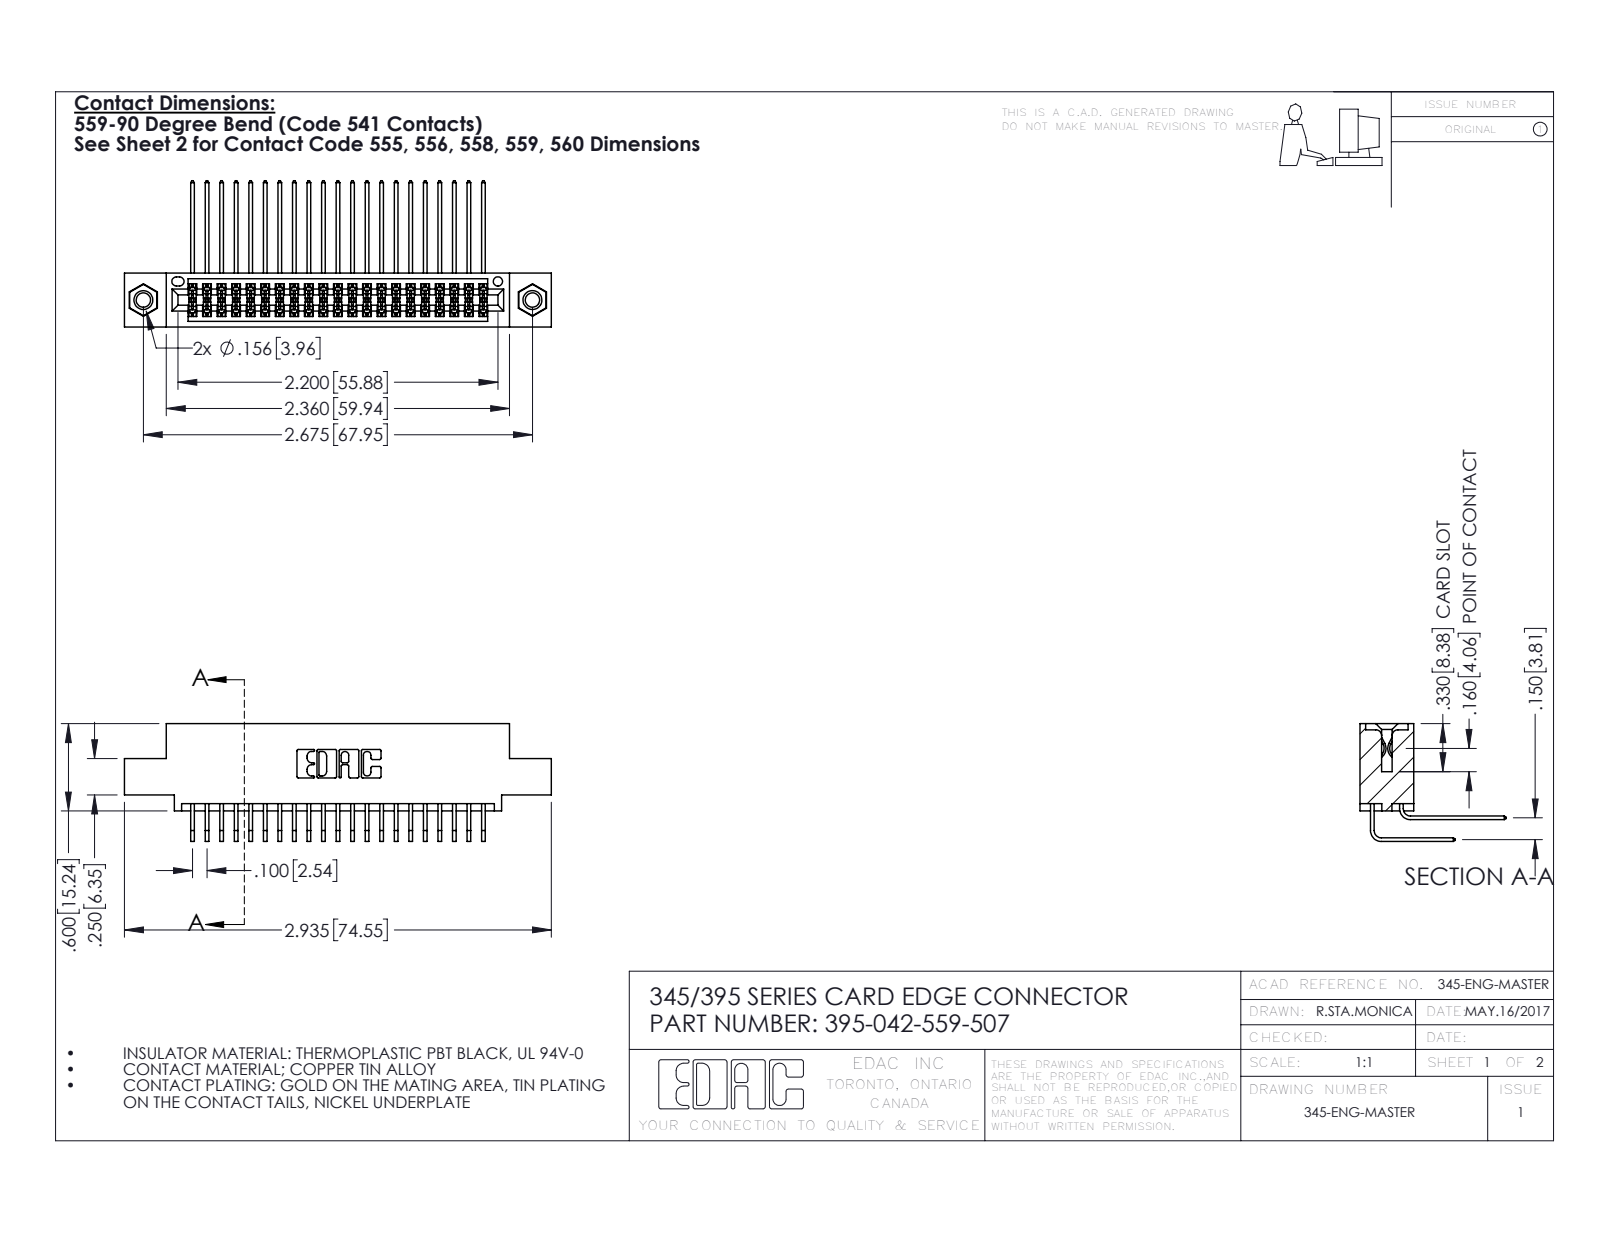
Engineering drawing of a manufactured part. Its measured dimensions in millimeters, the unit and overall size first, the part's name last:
Units: millimetres
Overall size (bounding box): 74.5 × 25.5 × 20.5
Round holes (diameter × count): ⌀2.5 ×2, ⌀3.2 ×2, ⌀4 ×2, ⌀1.6 ×1
Round bosses / shafts (diameter × count): ⌀3.9 ×2
Partial cylindrical surfaces — rounded edges, fillets, slot ends (radius × count): R0.2 ×63, R0.3 ×22, R0.2 ×6, R0.8 ×6, R0.7 ×3, R0.4 ×2, R0.5 ×2, R0.6 ×2
Main face-to-face distances: 1.8, 7.6, 5.1, 9.4, 2.5, 6.9, 0.6, 5.7, 3.8, 4.4
Hole centre spacings: 6.9, 62, 67.9
Volume: 7 210 mm³ · Surface area: 11 500 mm²
Bodies: 45 solids, 2374 faces (1586 planar, 772 cylindrical, 16 other)
Part name (STEP PRODUCT): 345-292-001_559 Tail - 2; 345 Part_0.110 Offset - 0.156 Dia-TI; 395-042-559-507; 345-292-001_558 559 Tail - 1 (+1 more)
STEP written by: SolidWorks 2016 (CONFIG_CONTROL_DESIGN)
